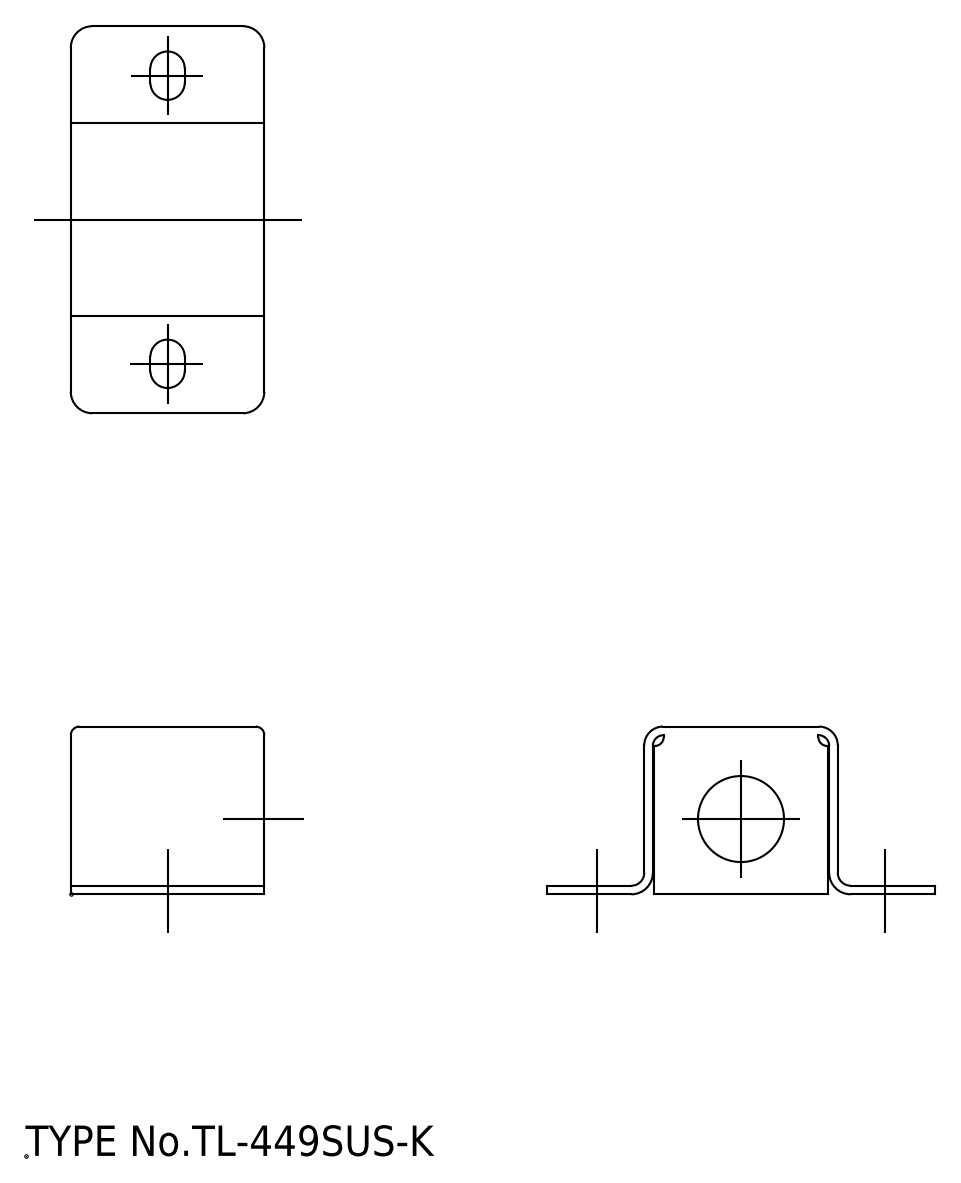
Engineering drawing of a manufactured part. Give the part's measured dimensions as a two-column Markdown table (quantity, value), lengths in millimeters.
| quantity | value |
| --- | --- |
| STEP written by | spGate 19.8.4 (****-****-****-****) (AUTOMOTIVE_DESIGN) |
| units | millimeters |
| bodies | 1 solid, 39 faces (19 planar, 20 cylindrical, 0 other) |
| overall size | 36 × 18 × 15.6 |
| volume | 1 232 mm³ |
| surface area | 3 204 mm² |
| round holes (diameter × count) | 8 × 1 |
| partial cylindrical surfaces (radius × count) | 2 × 6, 1.6 × 4, 0.8 × 2, 0.95 × 2, 1.2 × 2, 1.75 × 2 |
| main face-to-face distances | 0.8, 17.2, 14.8, 18, 16.4, 15.6, 14, 9.8, 9, 26.2 |
